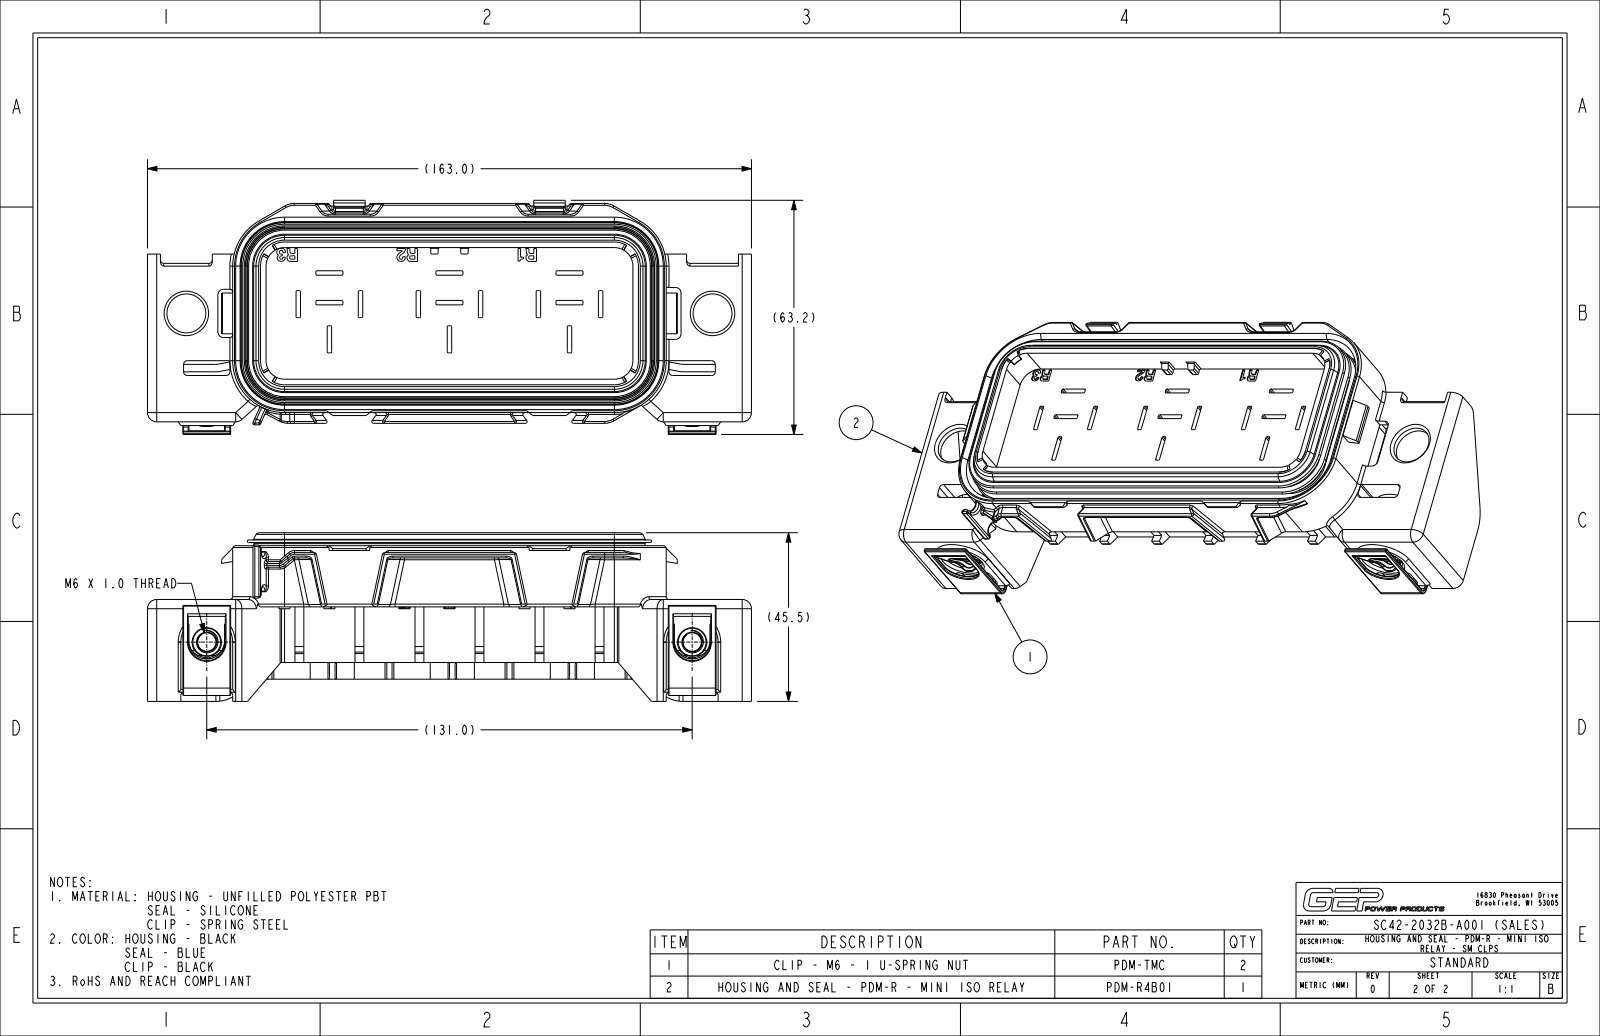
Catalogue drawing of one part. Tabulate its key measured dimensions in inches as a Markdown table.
| quantity | value |
| --- | --- |
| part name | C26-1012-2B_SALES_NCF; C14-1013_INSTALLED_NCF; PDM-RS_INSTALLED_NCF_ASM; PDM-R4B01_NCF_ASM (+3 more) |
| STEP written by | CREO PARAMETRIC BY PTC INC, 2024014 (CONFIG_CONTROL_DESIGN) |
| units | inches |
| bodies | 4 solids, 3170 faces (1364 planar, 954 cylindrical, 852 other) |
| overall size | 6.417 × 2.487 × 1.791 |
| volume | 6.246 in³ |
| surface area | 161.3 in² |
| round holes (diameter × count) | 0.413 × 4, 0.197 × 2, 0.295 × 2, 0.492 × 2 |
| round bosses / shafts (diameter × count) | 0.276 × 2, 0.197 × 1, 0.098 × 1 |
| partial cylindrical surfaces (radius × count) | 0.02 × 241, 0.012 × 106, 0.008 × 68, 0.079 × 50, 0.035 × 39, 0.018 × 38, 0.167 × 30, 0.039 × 26 |
| main face-to-face distances | 0.059, 0.079, 0.453, 0.374, 1.457, 1.516, 0.217, 0.071, 0.394, 0.276 |
| hole center spacings | 5.157, 5.591 |
